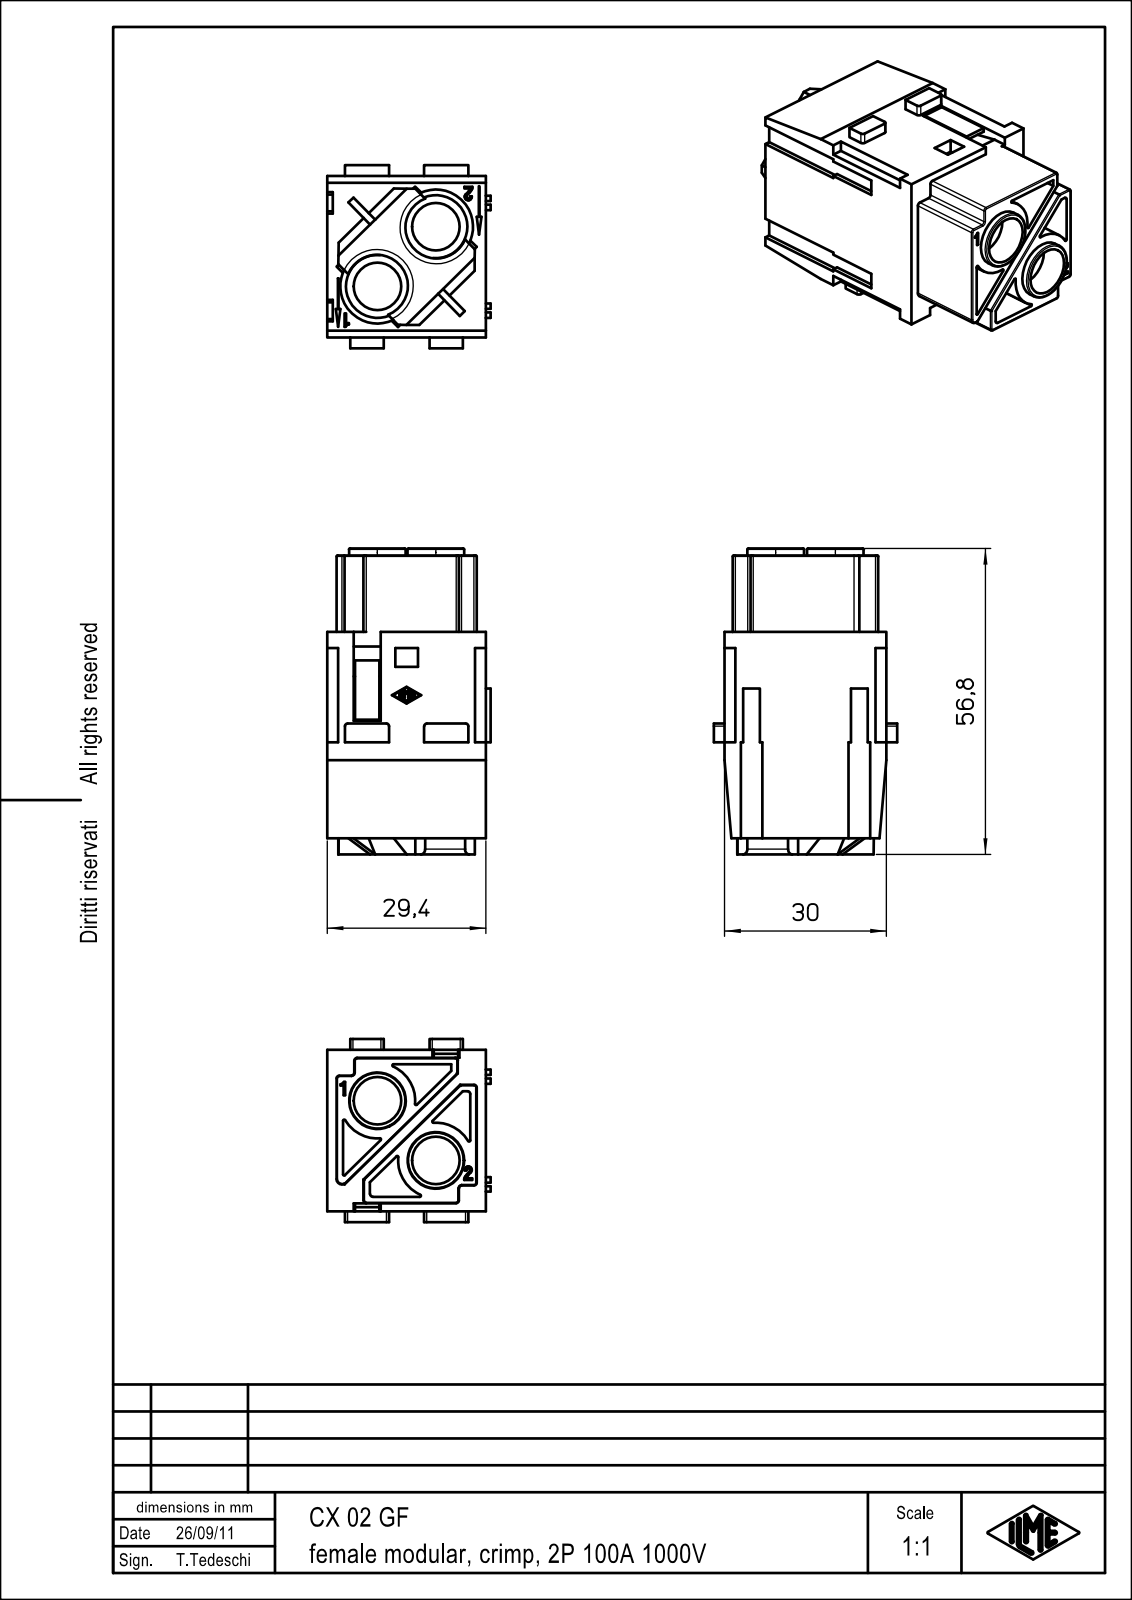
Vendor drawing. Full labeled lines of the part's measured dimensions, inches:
Part name (STEP PRODUCT): CX_02_GF
STEP written by: Creo Elements/Direct Modeling 17.0C 05-Feb-2011 (C) Parametric Technology GmbH (AUTOMOTIVE_DESIGN)
Units: inches
Bodies: 1 solid, 466 faces (363 planar, 78 cylindrical, 25 other)
Overall size (bounding box): 2.236 × 1.339 × 1.193
Volume: 1.602 in³ · Surface area: 25.61 in²
Round holes (diameter × count): ⌀0.346 ×2, ⌀0.461 ×2, ⌀0.543 ×2
Round bosses / shafts (diameter × count): ⌀0.413 ×2
Partial cylindrical surfaces — rounded edges, fillets, slot ends (radius × count): R0.008 ×23, R0.02 ×19, R0.004 ×5, R0.226 ×2, R0.276 ×2, R0.295 ×2, R0.315 ×2, R0.039 ×1
Main face-to-face distances: 1.157, 0.047, 0.118, 0.059, 1.181, 0.067, 1.122, 1.091, 0.079, 1.043
Hole centre spacings: 0.61
